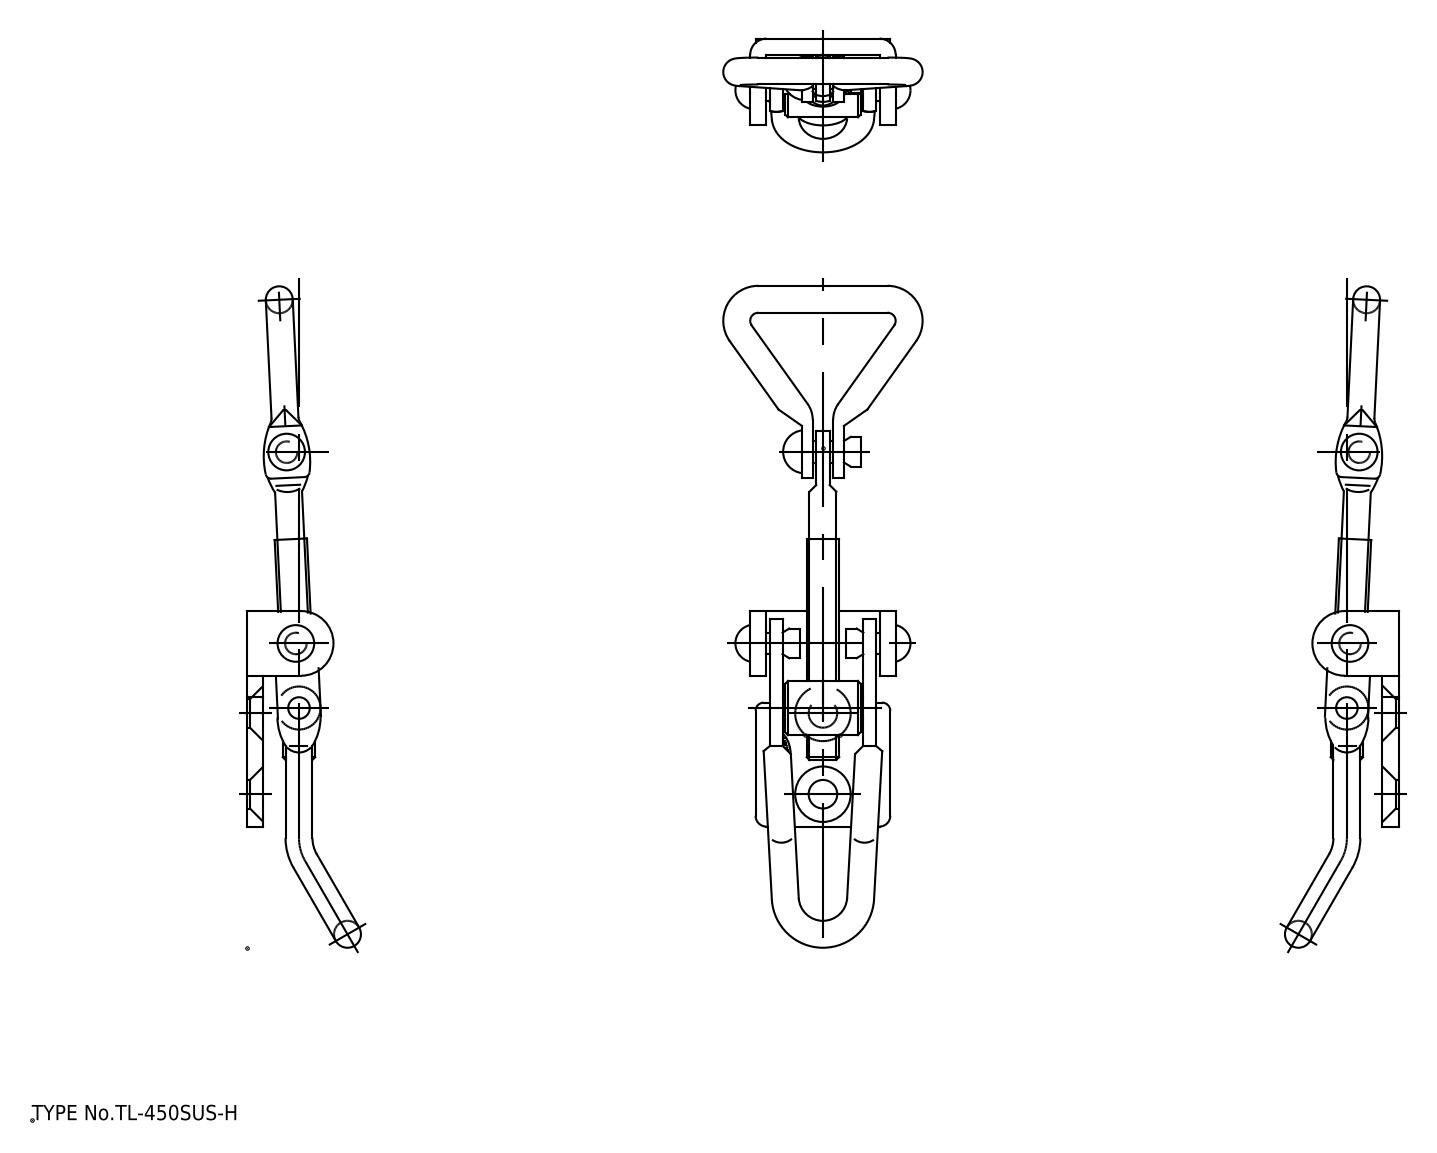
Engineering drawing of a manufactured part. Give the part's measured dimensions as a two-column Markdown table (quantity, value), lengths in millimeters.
| quantity | value |
| --- | --- |
| part name | アーム; ソケット; ベース; ボルト (+1 more) |
| STEP written by | spGate 19.8.4 (****-****-****-****) (AUTOMOTIVE_DESIGN) |
| units | millimeters |
| bodies | 5 solids, 198 faces (64 planar, 82 cylindrical, 52 other) |
| overall size | 120.54 × 37 × 21.1 |
| volume | 10 673 mm³ |
| surface area | 9 343 mm² |
| round holes (diameter × count) | 4 × 3, 5.3 × 2, 6 × 1 |
| round bosses / shafts (diameter × count) | 5 × 8, 10 × 1, 6 × 1, 5.5 × 1 |
| partial cylindrical surfaces (radius × count) | 1 × 4, 2 × 4, 0.5 × 2, 0.88 × 2, 1.5 × 2, 3 × 2, 5 × 2, 8 × 2 |
| main face-to-face distances | 3, 21, 2.3, 17.3, 0.7, 18, 20.3, 8.6, 2, 14.4 |
| hole center spacings | 12, 15, 33.35, 45.33 |
